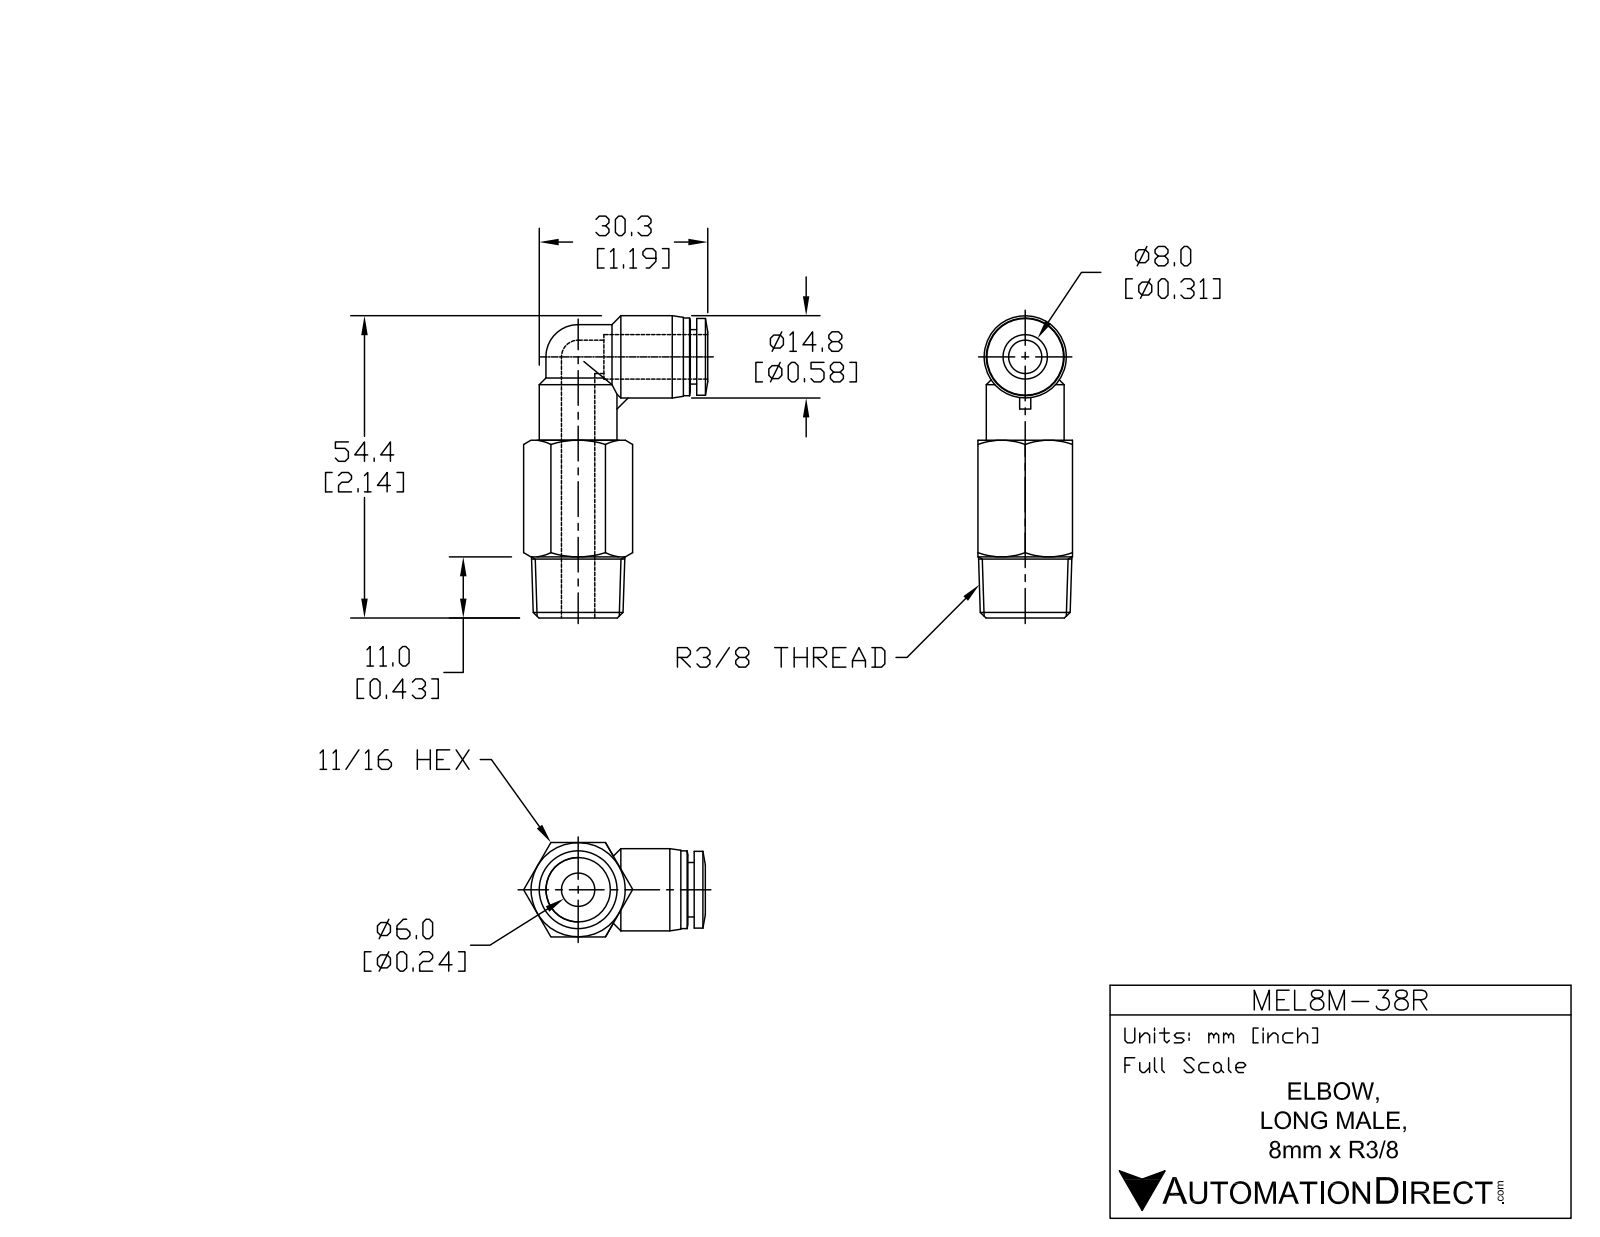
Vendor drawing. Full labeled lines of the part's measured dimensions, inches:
Part name (STEP PRODUCT): MEL8M-38R
STEP written by: SolidWorks 2015 (AUTOMOTIVE_DESIGN)
Units: inches
Bodies: 1 solid, 69 faces (17 planar, 19 cylindrical, 33 other)
Overall size (bounding box): 2.142 × 1.288 × 0.669
Volume: 0.636 in³ · Surface area: 8.278 in²
Round holes (diameter × count): ⌀0.236 ×2, ⌀0.327 ×1
Round bosses / shafts (diameter × count): ⌀0.551 ×2, ⌀0.583 ×1, ⌀0.543 ×1, ⌀0.457 ×1, ⌀0.386 ×1
Partial cylindrical surfaces — rounded edges, fillets, slot ends (radius × count): R0.228 ×1
Main face-to-face distances: 0.669, 1.26, 0.045, 0.596, 0.642, 0.079, 0.72, 0.124, 0.433, 0.827
